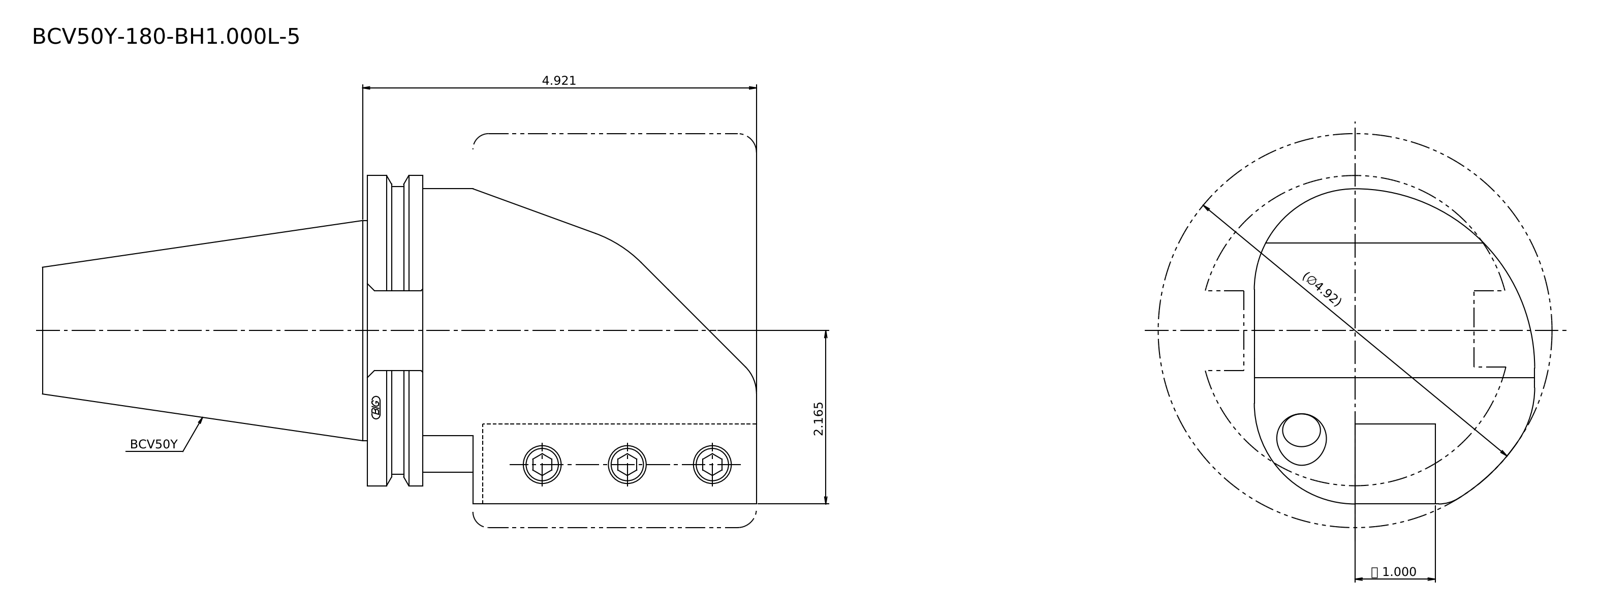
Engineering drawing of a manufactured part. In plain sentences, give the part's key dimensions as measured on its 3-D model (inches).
Its 3-D file was written by "Kubotek KeyCreator 2011 V10.0.2 (22737) (automotive_design)". It is 1 solid with 31 faces: 16 planar, 11 cylindrical and 4 other. Overall it measures 226.6 by 106.213 by 104.213 inches. Its volume is 960 323 cubic inches and its surface area 72 648 square inches. Round bosses or shafts: 1 of diameter 98.425, 1 of diameter 91.29, 1 of diameter 69.85. Partial cylindrical surfaces (rounded edges, fillets, slot ends): 2 of radius 32, 1 of radius 12, 1 of radius 30, 1 of radius 45, 1 of radius 57, 1 of radius 62.5. The main face-to-face distances are 25.4, 123.5, 32, 57.4, 105.95, 17.55, 90, 15.95, 33.5, 226.6.
